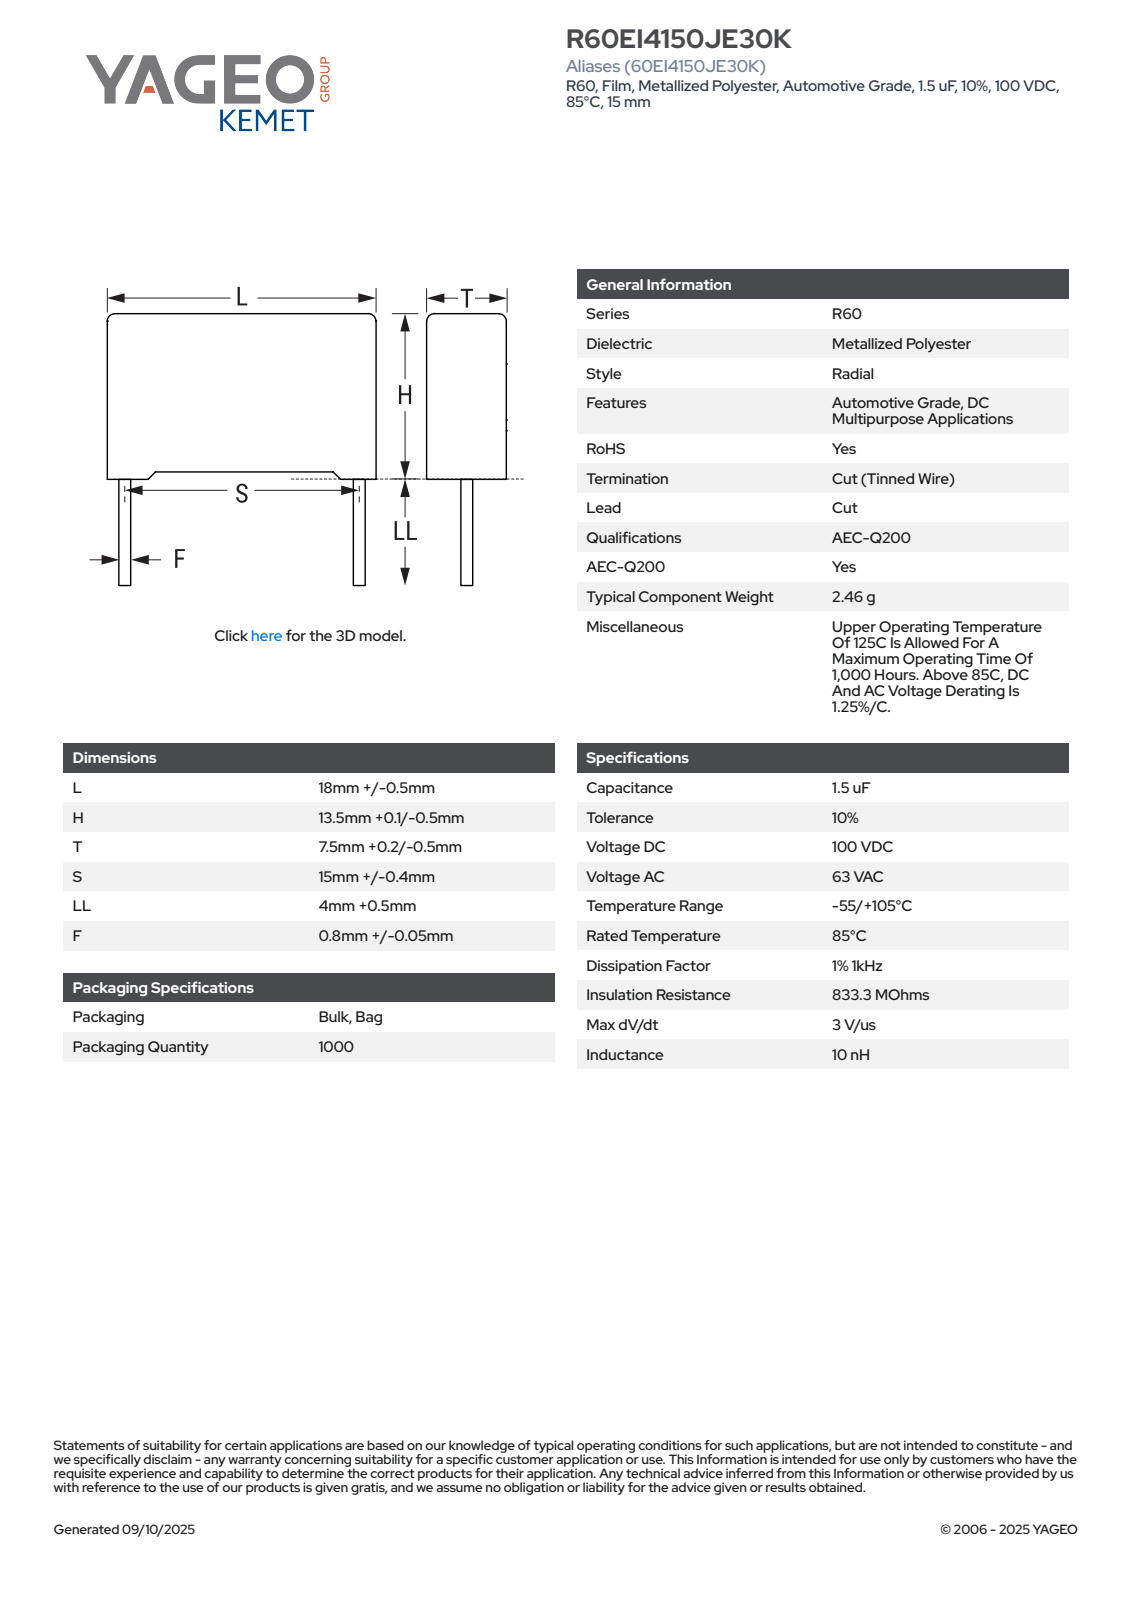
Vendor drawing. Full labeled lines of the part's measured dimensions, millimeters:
Part name (STEP PRODUCT): CFR_RB2_18X13.5X7.5_L18.5H13.6T7.7S15LL4.5F0.85
STEP written by: SolidWorks 2021 (AUTOMOTIVE_DESIGN)
Units: millimetres
Bodies: 4 solids, 85 faces (77 planar, 8 cylindrical, 0 other)
Overall size (bounding box): 18.5 × 18.1 × 7.71
Volume: 1 850 mm³ · Surface area: 1 054 mm²
Round bosses / shafts (diameter × count): ⌀0.85 ×2
Partial cylindrical surfaces — rounded edges, fillets, slot ends (radius × count): R0.5 ×4
Main face-to-face distances: 7.7, 12.85, 18.5, 0.62, 0.75, 13.6, 7.08, 0.47, 13.13, 17.88
